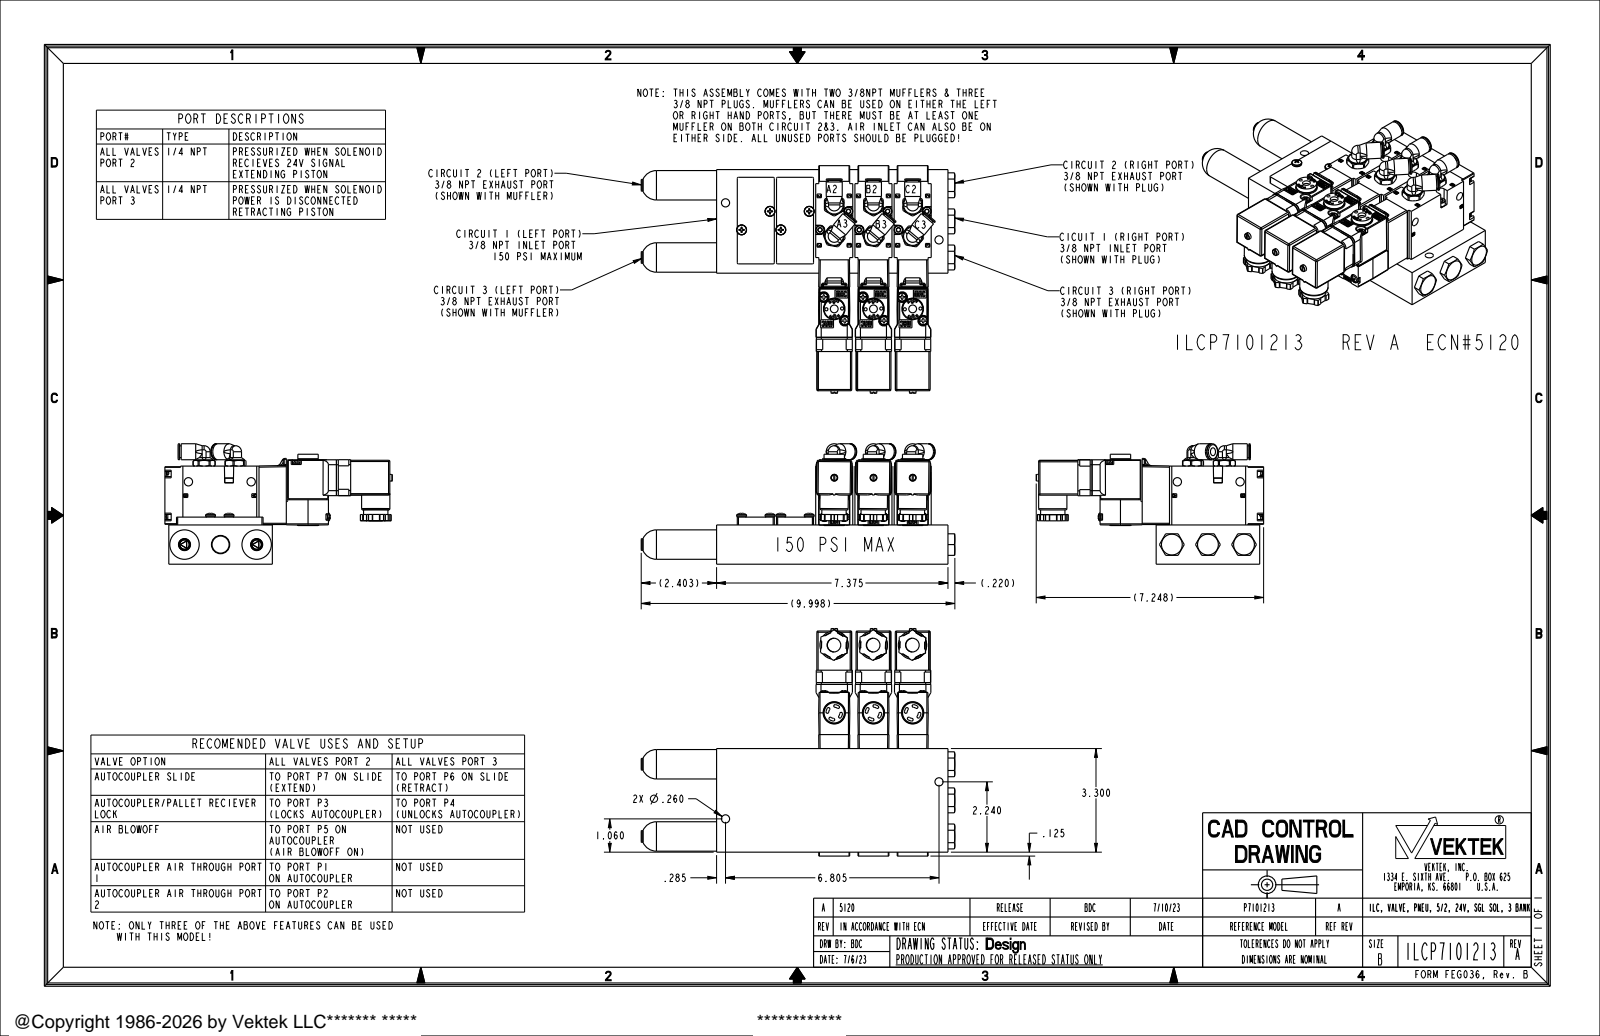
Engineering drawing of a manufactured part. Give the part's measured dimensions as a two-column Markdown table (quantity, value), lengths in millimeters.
| quantity | value |
| --- | --- |
| part name | ILCP7101213 |
| STEP written by | CREO PARAMETRIC BY PTC INC, 2021164 (AUTOMOTIVE_DESIGN) |
| units | millimeters |
| bodies | 4 solids, 4233 faces (2260 planar, 1010 cylindrical, 963 other) |
| overall size | 253.9 × 184.1 × 97.5 |
| volume | 1 233 000 mm³ |
| surface area | 186 900 mm² |
| round holes (diameter × count) | 3.5 × 12, 6.4 × 12, 2.5 × 6, 2.8 × 6, 3.2 × 6, 6.5 × 6, 7.3 × 6, 2.7 × 3, 2.8 × 3, 6 × 3, 6.3 × 3, 11.1 × 3 |
| round bosses / shafts (diameter × count) | 7 × 18, 6.5 × 12, 9.5 × 8, 16.5 × 6, 14.8 × 6, 13 × 6, 6.8 × 6, 22.9 × 3 |
| partial cylindrical surfaces (radius × count) | 0.2 × 72, 1 × 60, 0.4 × 48, 0.3 × 42, 0.5 × 37, 4 × 36, 0.8 × 33, 0.9 × 24 |
| main face-to-face distances | 31.8, 63.5, 30, 83.8, 31.8, 61.7, 1.8, 27.5, 0.5, 2.5 |
| hole center spacings | 31.8, 63.5, 26.2, 53.4, 12.9, 13.1, 14.8, 25.4 |
